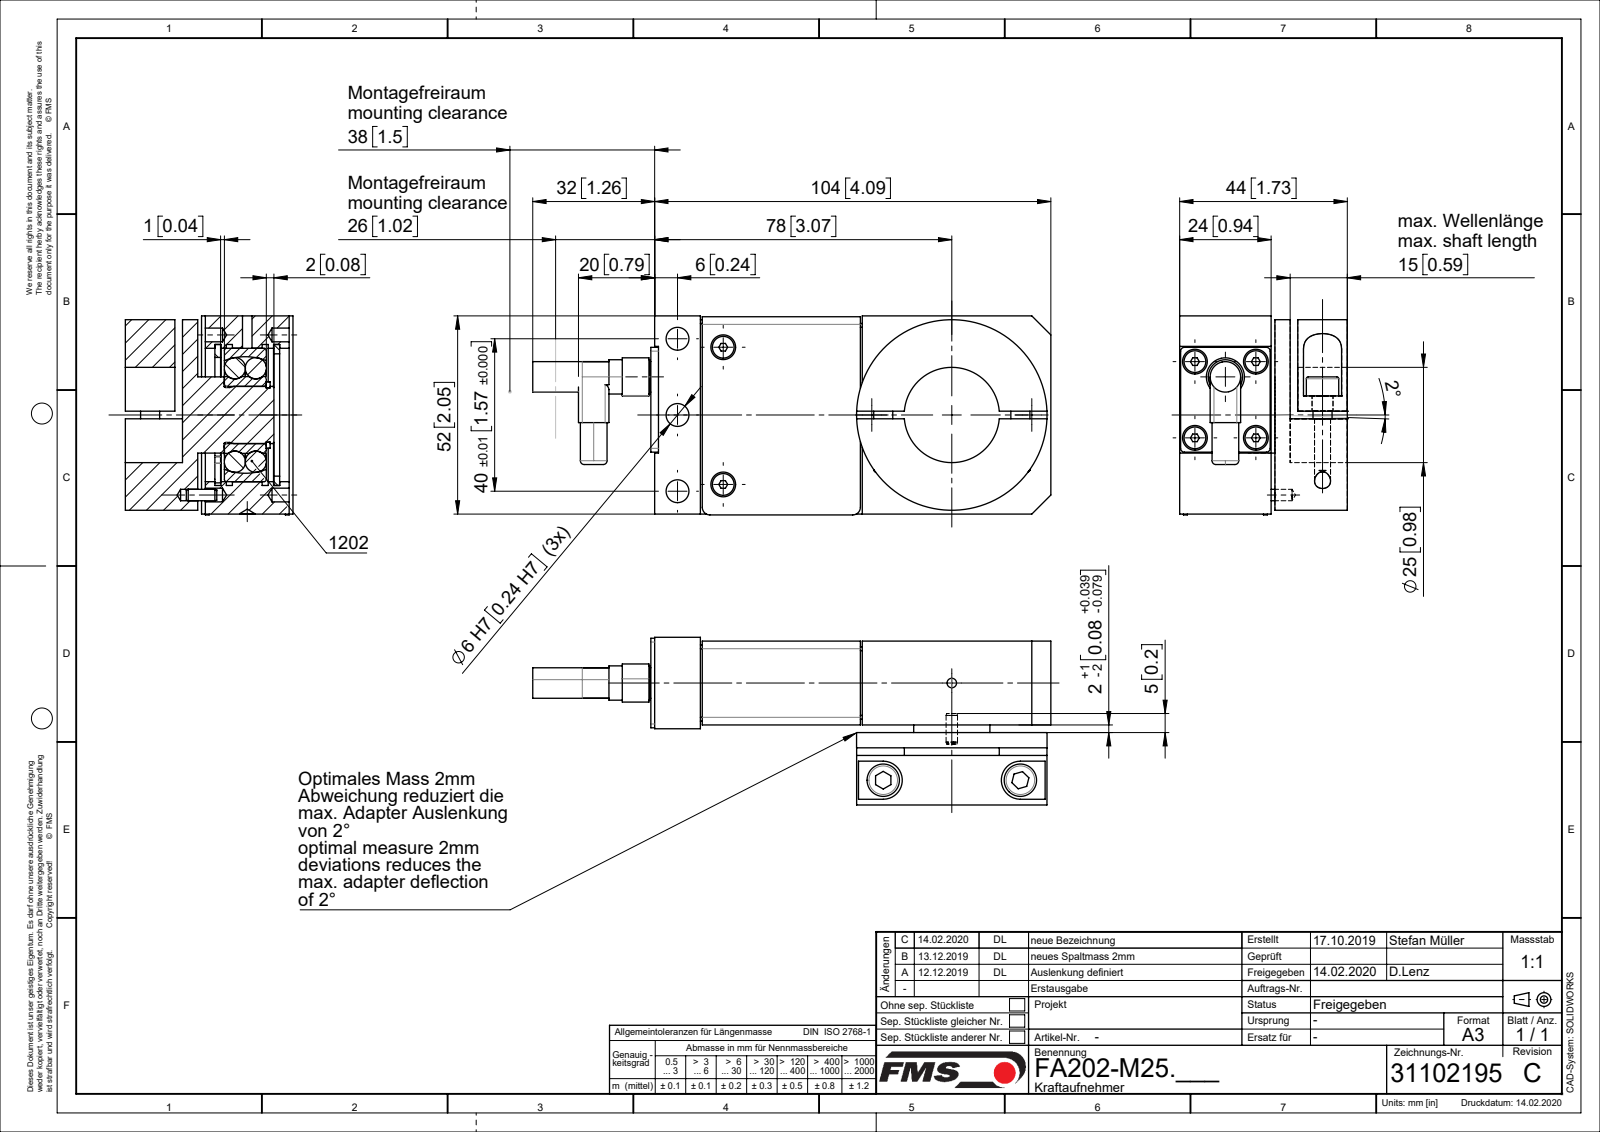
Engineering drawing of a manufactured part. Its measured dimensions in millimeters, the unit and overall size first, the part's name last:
Units: millimetres
Overall size (bounding box): 123 × 52 × 50
Round holes (diameter × count): ⌀2.6 ×7, ⌀1 ×4, ⌀3.2 ×4, ⌀3.6 ×4, ⌀6 ×4, ⌀4.33 ×2, ⌀5.5 ×2, ⌀3 ×1, ⌀4 ×1, ⌀6.5 ×1, ⌀7 ×1, ⌀14.3 ×1
Round bosses / shafts (diameter × count): ⌀6 ×7, ⌀3 ×6, ⌀1 ×4, ⌀8 ×3, ⌀10 ×2, ⌀5 ×2, ⌀50 ×1, ⌀22.6 ×1
Partial cylindrical surfaces — rounded edges, fillets, slot ends (radius × count): R2 ×8, R1 ×6, R5 ×2, R4.1 ×1
Main face-to-face distances: 1, 22, 21, 1.5, 2, 6, 2.5, 19, 18, 19.5
Hole centre spacings: 2.24, 20, 21, 29.7, 2, 10, 3.61, 7.21
Volume: 136 560 mm³ · Surface area: 59 102 mm²
Bodies: 26 solids, 606 faces (229 planar, 221 cylindrical, 156 other)
Part name (STEP PRODUCT): F0807306C_DM25; F0807304; F0807305; SENKSCHRAUBE_I-6KT_M3X6 (+8 more)
STEP written by: Mechanical Desktop 2009 (CONFIG_CONTROL_DESIGN)
